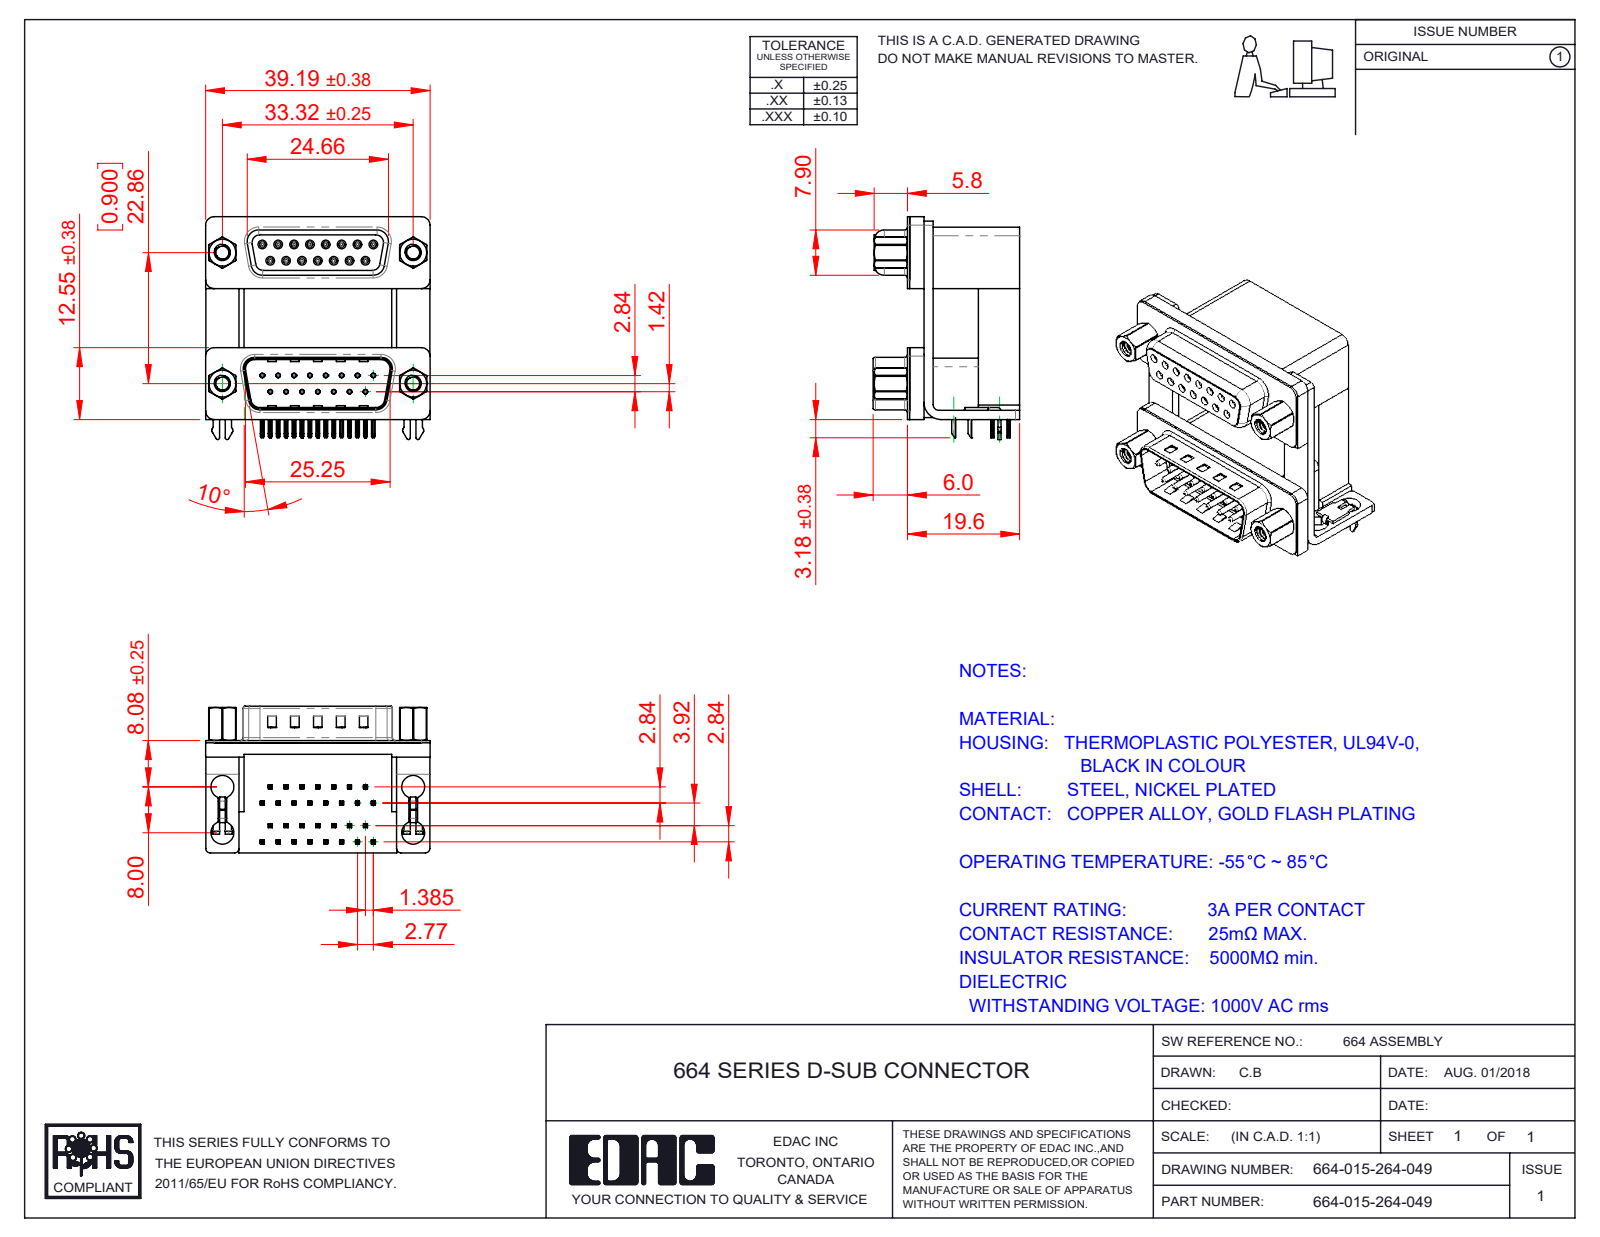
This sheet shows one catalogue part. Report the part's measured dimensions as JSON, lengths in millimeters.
{"part_name": "664 Shell Receptacle_15 Contacts; 664-015-264-049; 664 2 Prong Board Lock_4; 664 Threaded Rivet_4-40 (+8 more)", "step_written_by": "SolidWorks 2020 (CONFIG_CONTROL_DESIGN)", "units": "millimeters", "bodies": {"solids": 47, "faces": 4272, "planar": 2137, "cylindrical": 1188, "other": 947}, "overall_size": [39.19, 38.91, 25.6], "volume_mm3": 16358, "surface_area_mm2": 18676, "round_holes": [[0.8, 30], [0.35, 15], [0.9, 15], [4, 8], [2.26, 4], [2.29, 4], [3.5, 4], [4.8, 4], [5, 4]], "round_bosses_or_shafts": [[1.2, 15], [0.75, 15], [4.9, 4], [4.75, 4], [3.9, 4], [2.79, 4]], "partial_cylinders_radius": [[0.1, 121], [0.25, 66], [0.15, 60], [0.12, 30], [0.35, 30], [0.5, 16], [1.5, 16], [0.34, 15]], "face_to_face_distances": [0.4, 19.2, 12, 7.2, 16.7, 9.5, 2.5, 12.4, 2.19, 22.86], "hole_center_spacings": [3.16, 2.77, 23.03, 5.54, 23.52, 8.31, 22.86, 24.32]}
